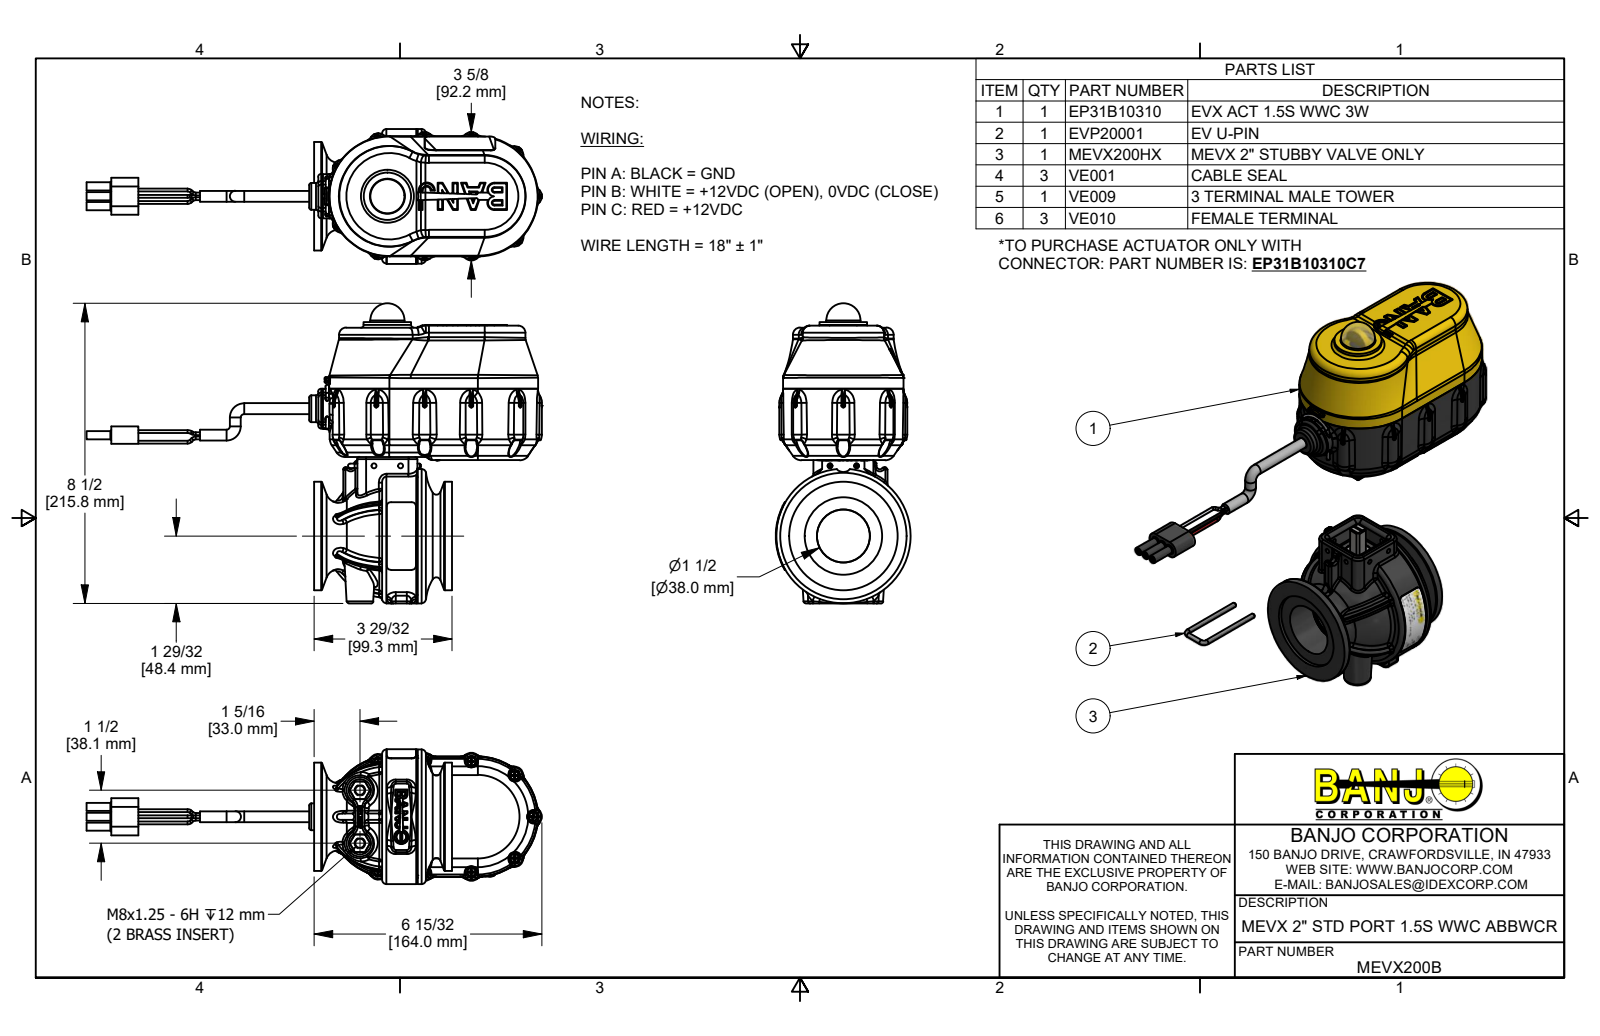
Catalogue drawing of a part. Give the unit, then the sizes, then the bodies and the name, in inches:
Units: inches
Overall size (bounding box): 12.901 × 8.497 × 3.823
Round holes (diameter × count): ⌀0.095 ×11, ⌀0.15 ×11, ⌀0.08 ×7, ⌀0.135 ×5, ⌀0.107 ×4, ⌀0.126 ×4, ⌀0.136 ×4, ⌀0.148 ×4, ⌀0.15 ×4, ⌀0.17 ×4, ⌀0.049 ×3, ⌀0.096 ×3
Round bosses / shafts (diameter × count): ⌀0.25 ×17, ⌀0.08 ×15, ⌀0.14 ×11, ⌀0.108 ×11, ⌀0.085 ×11, ⌀0.058 ×6, ⌀0.27 ×4, ⌀0.219 ×4
Partial cylindrical surfaces — rounded edges, fillets, slot ends (radius × count): R0.013 ×180, R0.04 ×145, R0.01 ×84, R0.02 ×71, R0.005 ×55, R0.06 ×43, R0.03 ×30, R0.08 ×28
Main face-to-face distances: 0.1, 2.565, 0.06, 0.211, 0.151, 1.896, 1.836, 1.685, 0.569, 0.629
Hole centre spacings: 2.023, 1.283, 2.69, 2.715, 0.75, 0.874, 0.946, 1.662
Volume: 51.62 in³ · Surface area: 593.1 in²
Bodies: 91 solids, 11103 faces (3087 planar, 3138 cylindrical, 4878 other)
Part name (STEP PRODUCT): MEVX200B; EP31B10310; B61905PPHS; B632038PM (+8 more)
STEP written by: Autodesk Inventor 2019 (AUTOMOTIVE_DESIGN)
